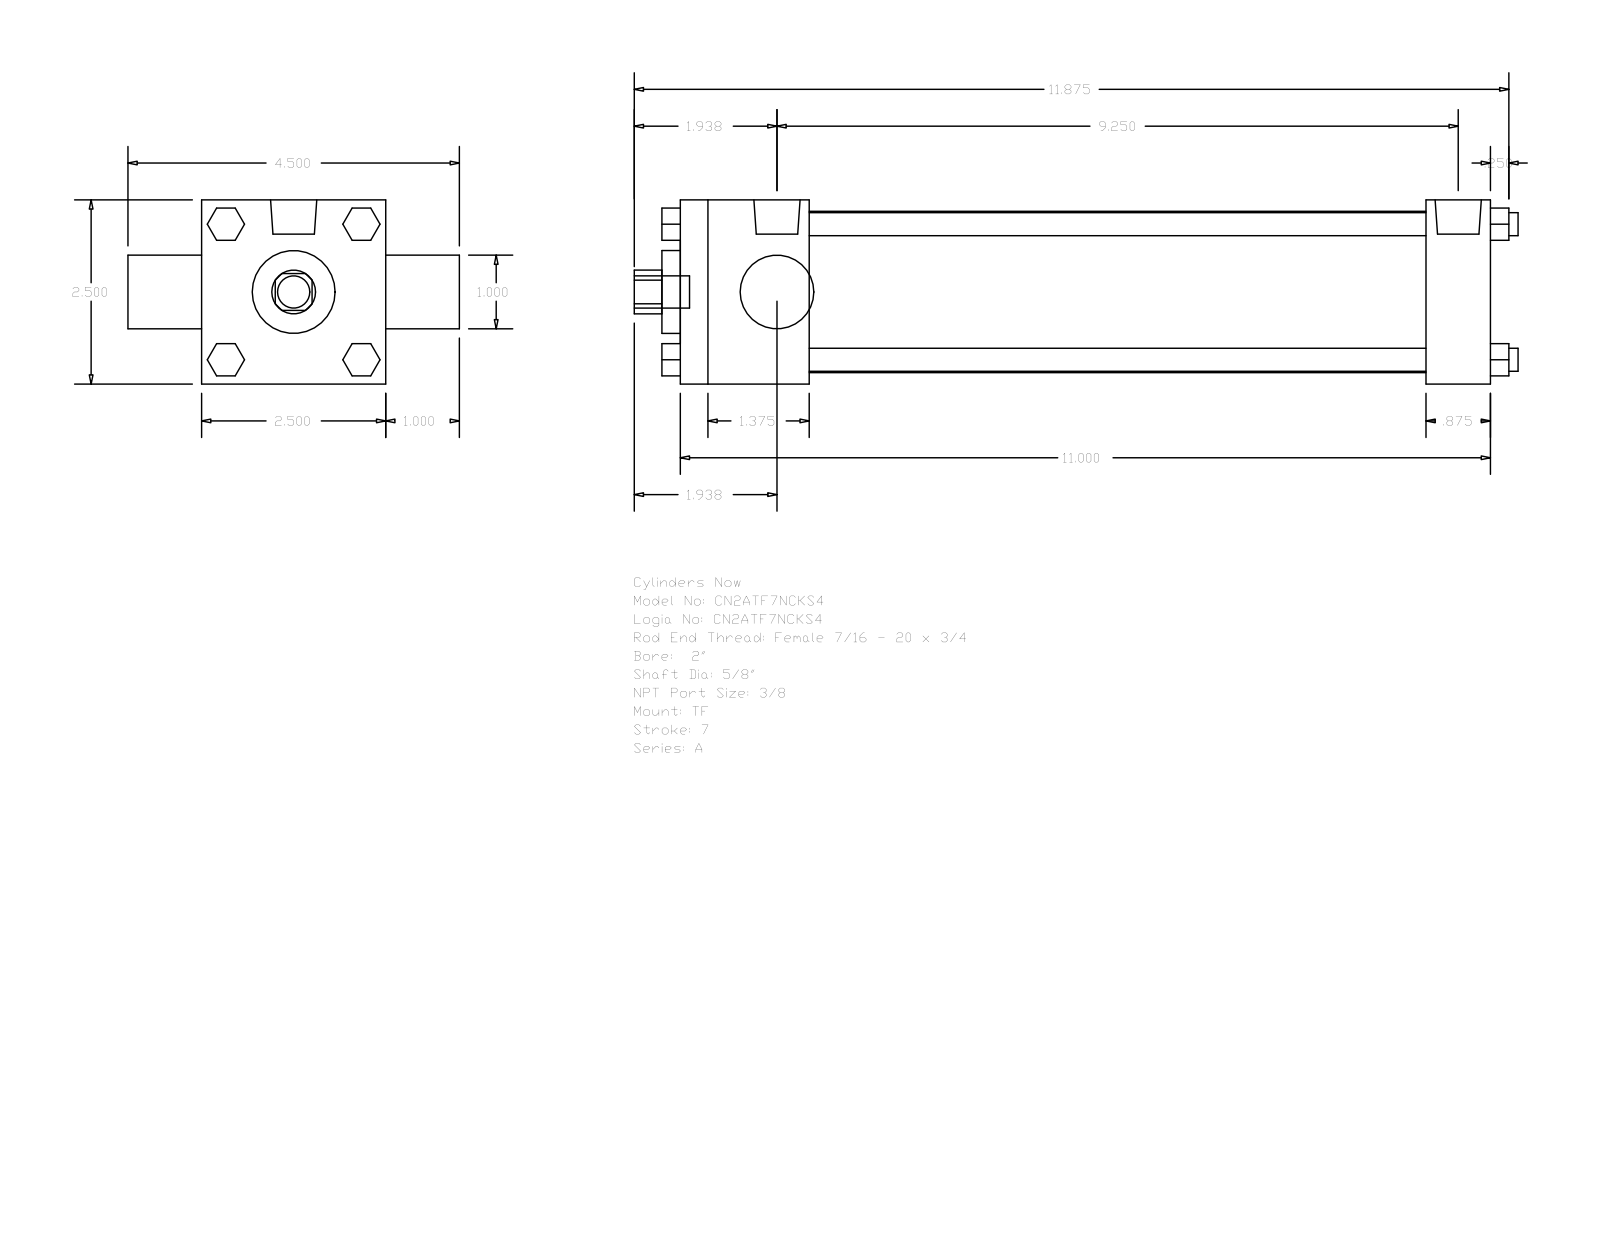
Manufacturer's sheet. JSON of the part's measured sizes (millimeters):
{"part_name": "A_TF__0200_0.625", "step_written_by": "GSSL Pune (CONFIG_CONTROL_DESIGN)", "units": "millimeters", "bodies": {"solids": 0, "faces": 120, "planar": 92, "cylindrical": 28, "other": 0}, "overall_size": [304.8, 114.3, 63.5], "round_holes": [[15.88, 1], [25.4, 1], [28.57, 1], [55.63, 1]], "round_bosses_or_shafts": [[7.94, 4], [5.56, 3], [15.93, 2], [11.11, 1]], "partial_cylinders_radius": [[7.54, 1]], "face_to_face_distances": [63.5, 279.39, 44.45, 257.17, 212.72, 234.94, 22.22, 25.4, 88.9, 6.35]}
